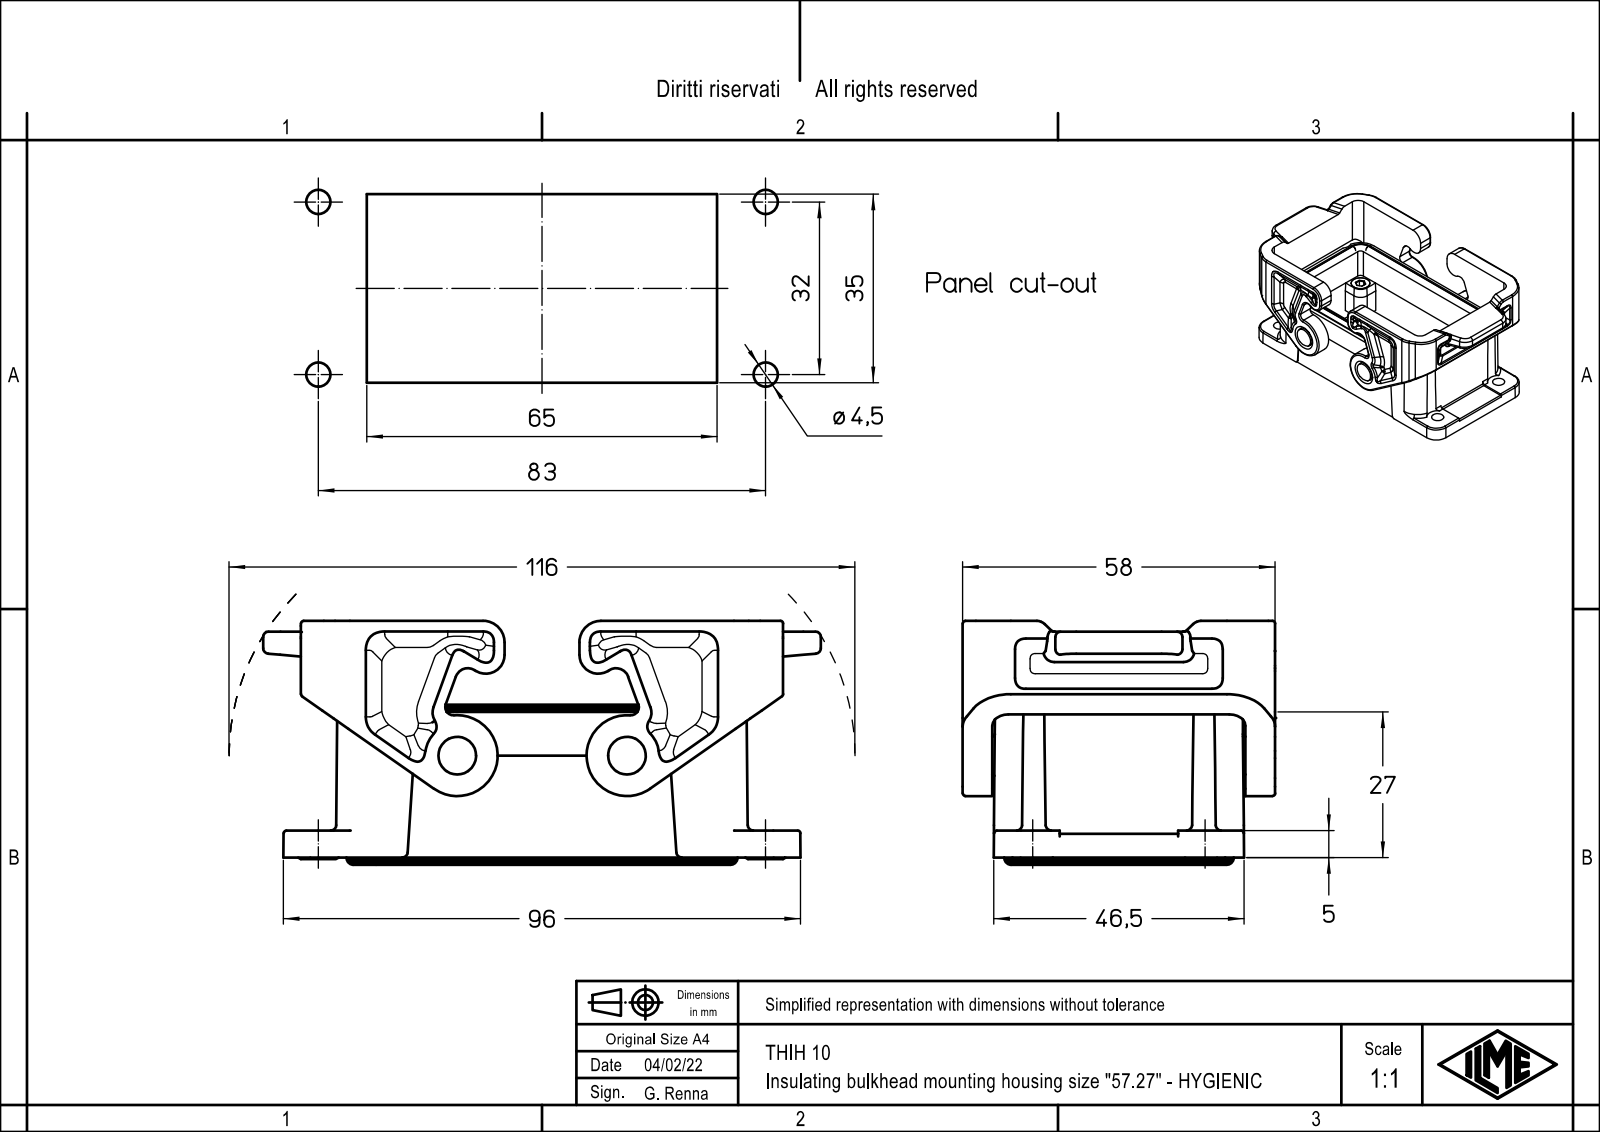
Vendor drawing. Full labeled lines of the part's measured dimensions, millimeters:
Part name (STEP PRODUCT): 53621; THIH_10
STEP written by: Creo Elements/Direct Modeling 20.1B 02-Apr-2019 (C) Parametric Technology GmbH (AUTOMOTIVE_DESIGN)
Units: millimetres
Bodies: 1 solid, 681 faces (300 planar, 213 cylindrical, 168 other)
Overall size (bounding box): 103.5 × 58 × 45.25
Volume: 64 343 mm³ · Surface area: 34 348 mm²
Round holes (diameter × count): ⌀2.5 ×4, ⌀4.5 ×4, ⌀7.2 ×2
Round bosses / shafts (diameter × count): ⌀4.8 ×4, ⌀7 ×2
Partial cylindrical surfaces — rounded edges, fillets, slot ends (radius × count): R1 ×25, R1.3 ×16, R2 ×12, R3 ×12, R5.5 ×12, R1.5 ×10, R5 ×8, R6 ×8
Main face-to-face distances: 40.6, 5.5, 52.5, 47, 70.61, 2, 43.9, 58, 5, 79.5
Hole centre spacings: 13.24, 32.24, 70.04, 75.96, 27, 32, 57, 63.07
